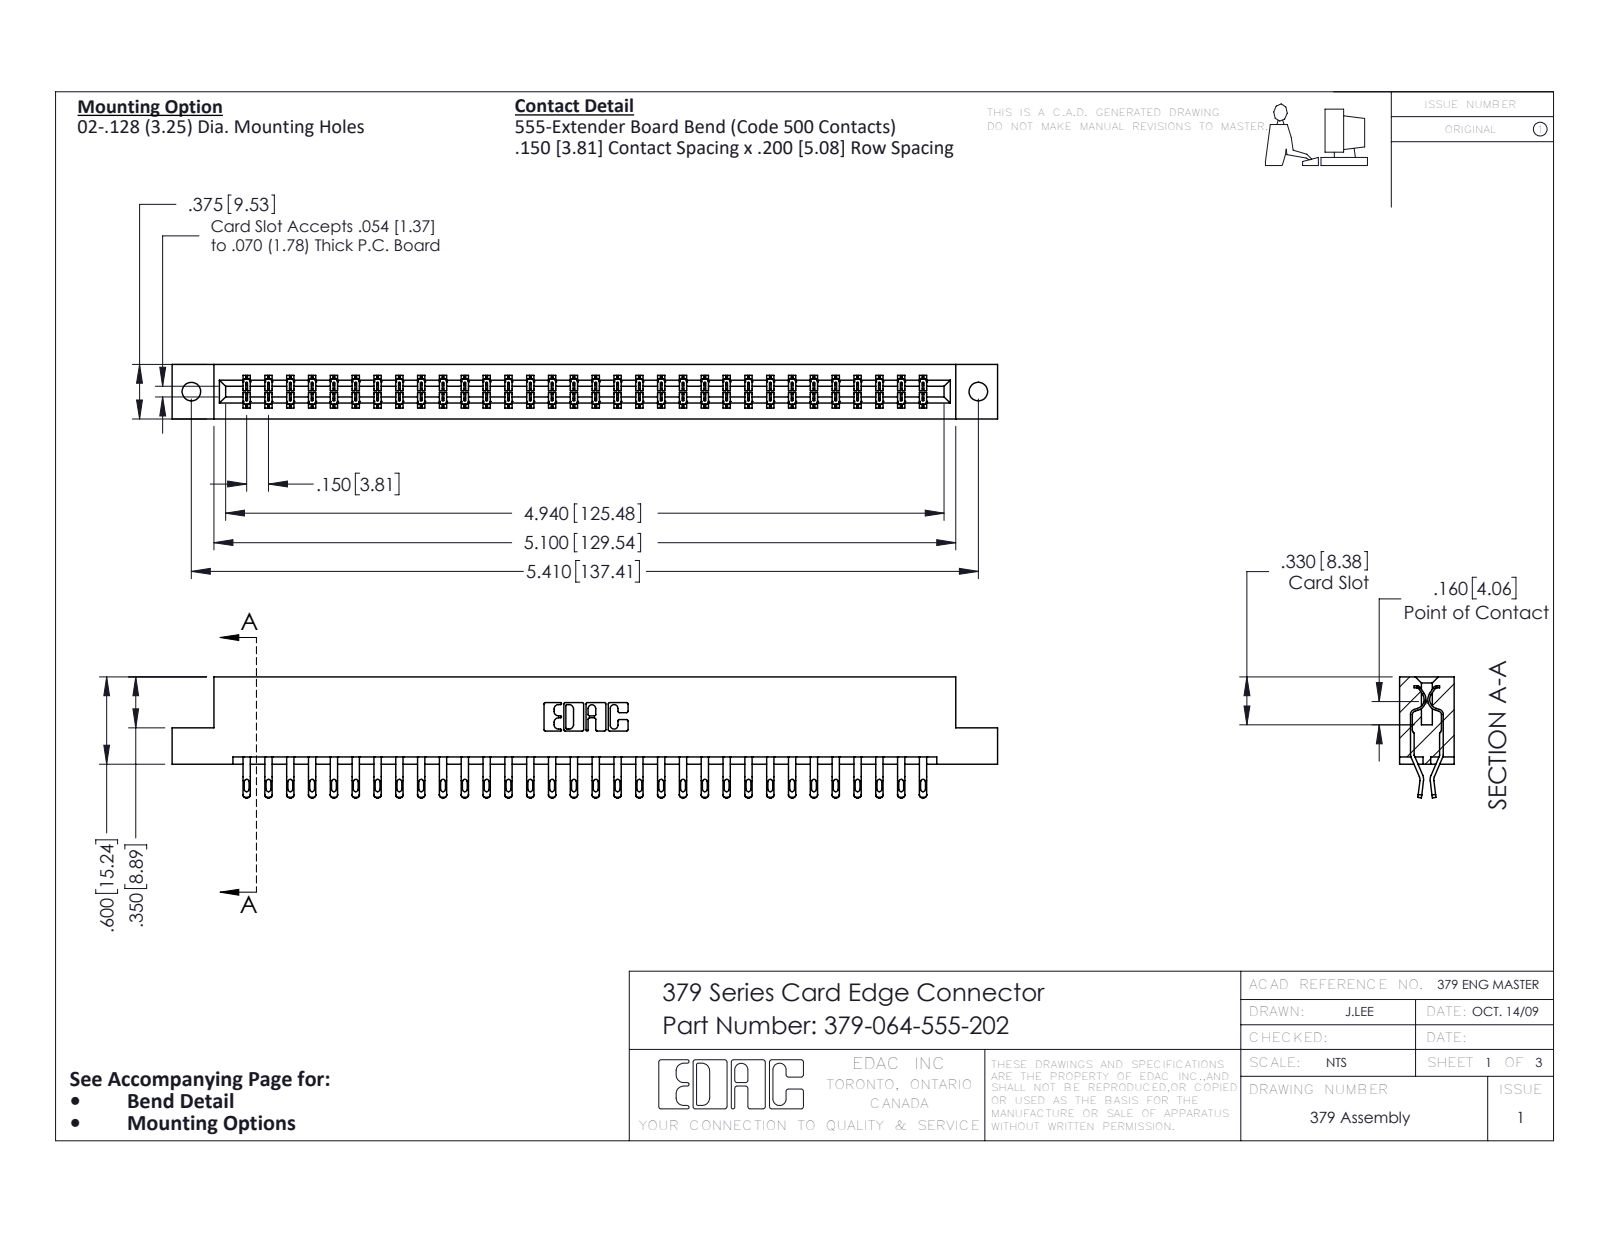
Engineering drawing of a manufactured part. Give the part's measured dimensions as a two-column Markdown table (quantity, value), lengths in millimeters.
| quantity | value |
| --- | --- |
| part name | 379 Part_Flush - .128 Dia; 379-064-555-202; 345-292-001_555 Tail |
| STEP written by | SolidWorks 2016 (CONFIG_CONTROL_DESIGN) |
| units | millimeters |
| bodies | 65 solids, 3826 faces (2246 planar, 1580 cylindrical, 0 other) |
| overall size | 144.1 × 21.1 × 9.5 |
| volume | 15 400 mm³ |
| surface area | 17 610 mm² |
| round holes (diameter × count) | 3.3 × 2 |
| partial cylindrical surfaces (radius × count) | 0.4 × 128, 0.5 × 128, 0.2 × 96, 0.3 × 22, 0.2 × 6, 0.8 × 6, 0.7 × 3, 0.3 × 2 |
| main face-to-face distances | 7.6, 1.9, 9.5, 5.1, 5.7, 2.5, 14, 0.6, 3.8, 1.9 |
| hole center spacings | 137.4 |
